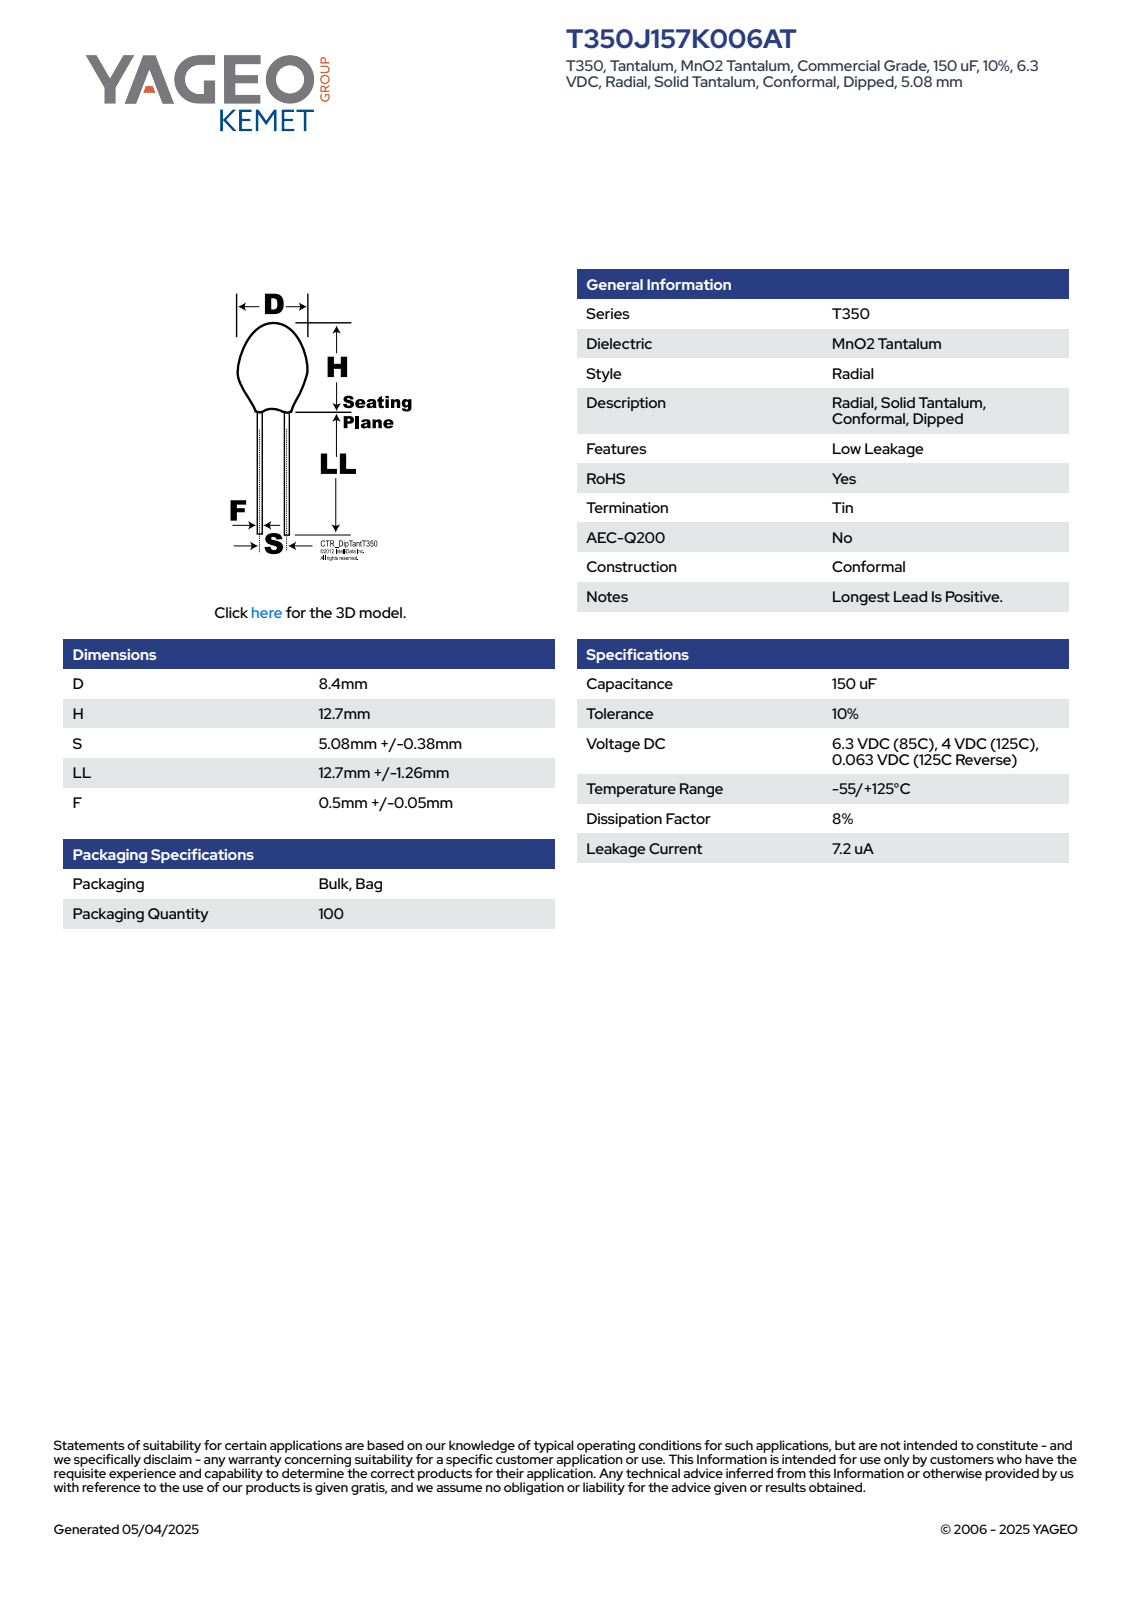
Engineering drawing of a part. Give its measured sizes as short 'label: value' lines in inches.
name: CTR_T350_D8.4H12.7S5.08LL13.96F0.55
written by: SolidWorks 2014 (AUTOMOTIVE_DESIGN)
unit: in
bodies: 1 solid, 73 faces (26 planar, 10 cylindrical, 37 other)
size: 1.05 × 0.331 × 0.331
volume: 0.035 in³; area: 0.625 in²
bosses: 2× ⌀0.022, 1× ⌀0.331
rounds: 1× R0.165
face distances: 0.5, 0.55, 1.05, 0.842, 0.292, 0.208, 0.794, 0.244, 0.048, 0.256
